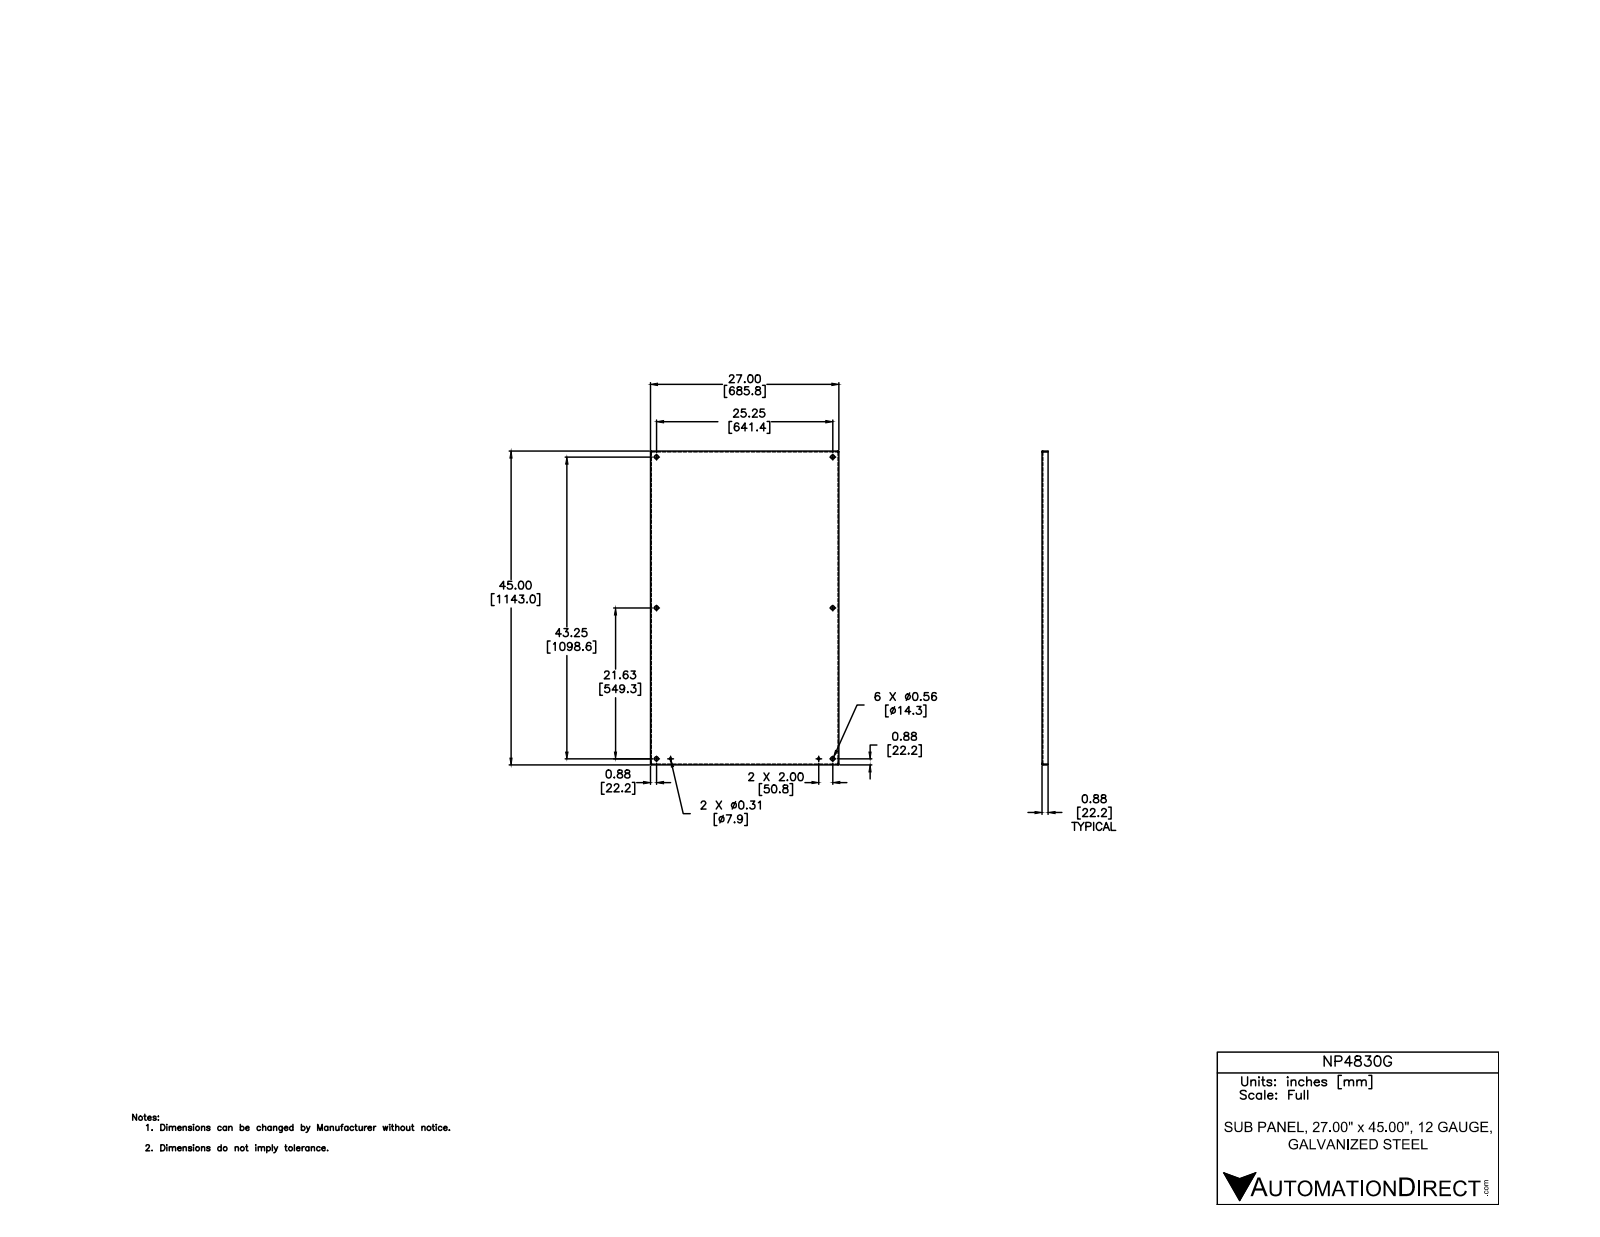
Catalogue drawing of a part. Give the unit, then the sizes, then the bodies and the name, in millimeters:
Units: millimetres
Overall size (bounding box): 1143 × 685.8 × 22.2
Round holes (diameter × count): ⌀14.3 ×6, ⌀7.9 ×2
Partial cylindrical surfaces — rounded edges, fillets, slot ends (radius × count): R0.8 ×4, R3.2 ×4
Main face-to-face distances: 2.4, 683.4, 1140.6, 681.1, 685.8, 1143, 1138.3, 19.8, 22.2, 2.7
Hole centre spacings: 844.4, 549.3, 549.3, 641.4, 1098.6, 1099.7, 1272.1, 50.8
Volume: 2 027 000 mm³ · Surface area: 1 714 000 mm²
Bodies: 1 solid, 46 faces (22 planar, 16 cylindrical, 8 other)
Part name (STEP PRODUCT): NP4830G
STEP written by: Autodesk Inventor 2012 (AUTOMOTIVE_DESIGN)
